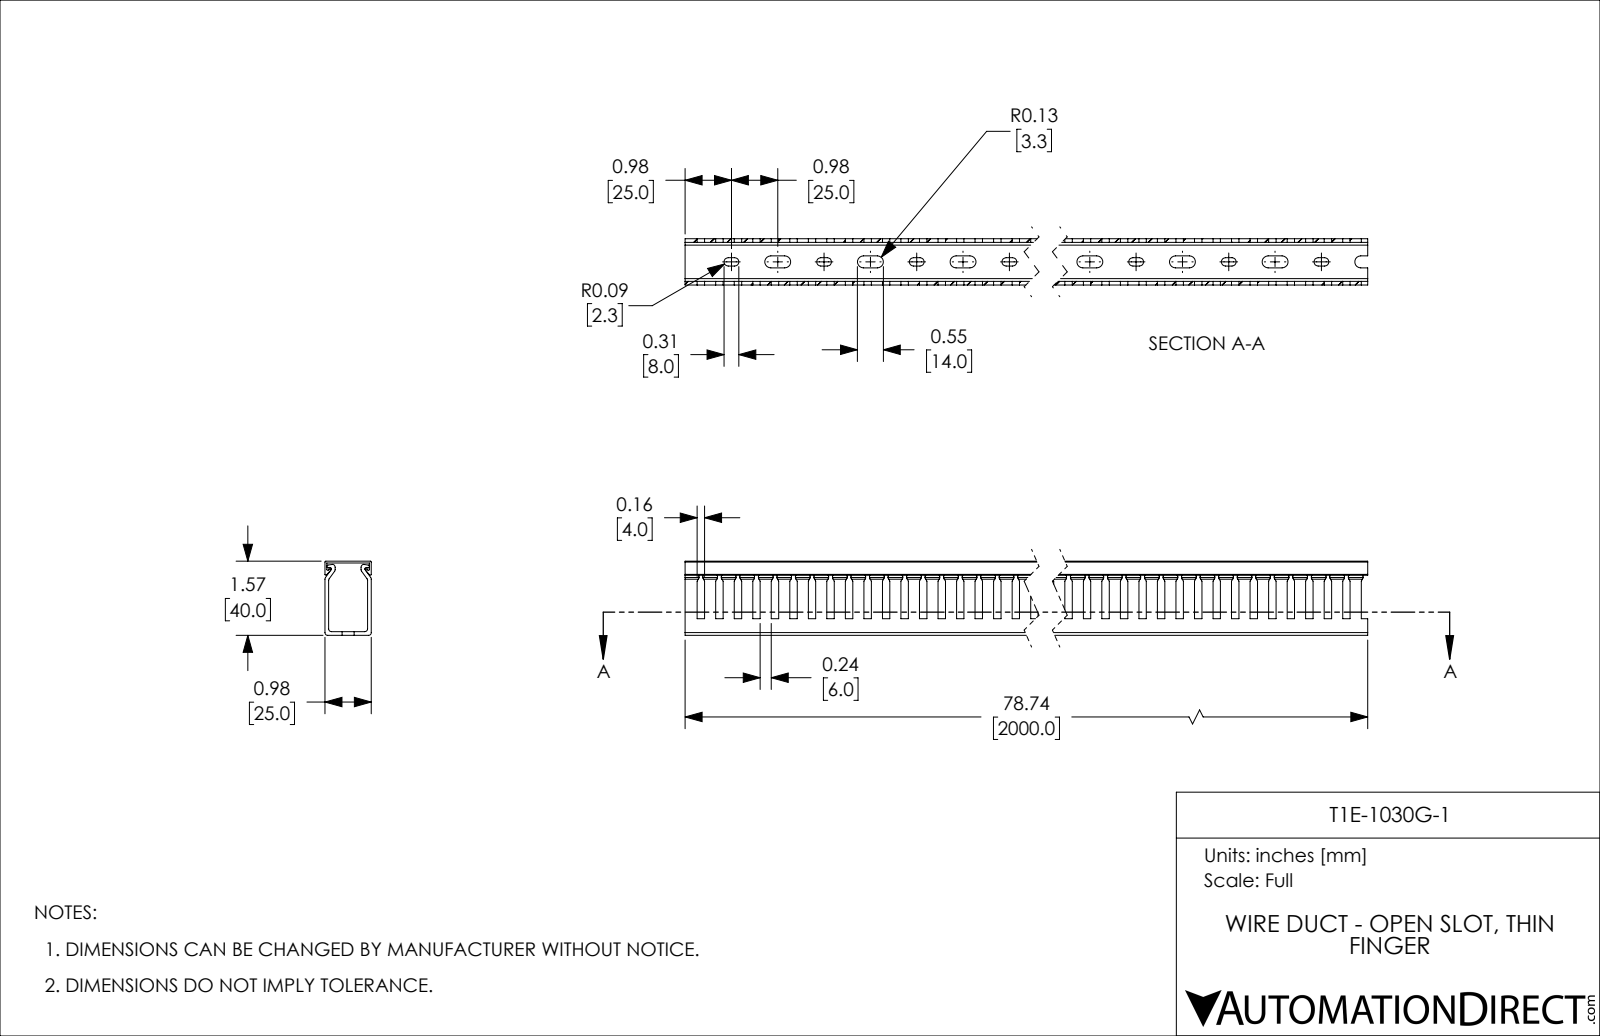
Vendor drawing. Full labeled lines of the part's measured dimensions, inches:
Part name (STEP PRODUCT): T1E-1015W-1
STEP written by: SolidWorks 2021 (CONFIG_CONTROL_DESIGN)
Units: inches
Bodies: 2 solids, 945 faces (514 planar, 431 cylindrical, 0 other)
Overall size (bounding box): 78.74 × 1.575 × 0.984
Volume: 29.71 in³ · Surface area: 894 in²
Partial cylindrical surfaces — rounded edges, fillets, slot ends (radius × count): R0.089 ×80, R0.128 ×80, R0.059 ×12, R0.02 ×8, R0.03 ×6
Main face-to-face distances: 0.079, 0.906, 0.039, 0.984, 0.827, 1.575, 1.535, 1.457, 1.496, 0.945
